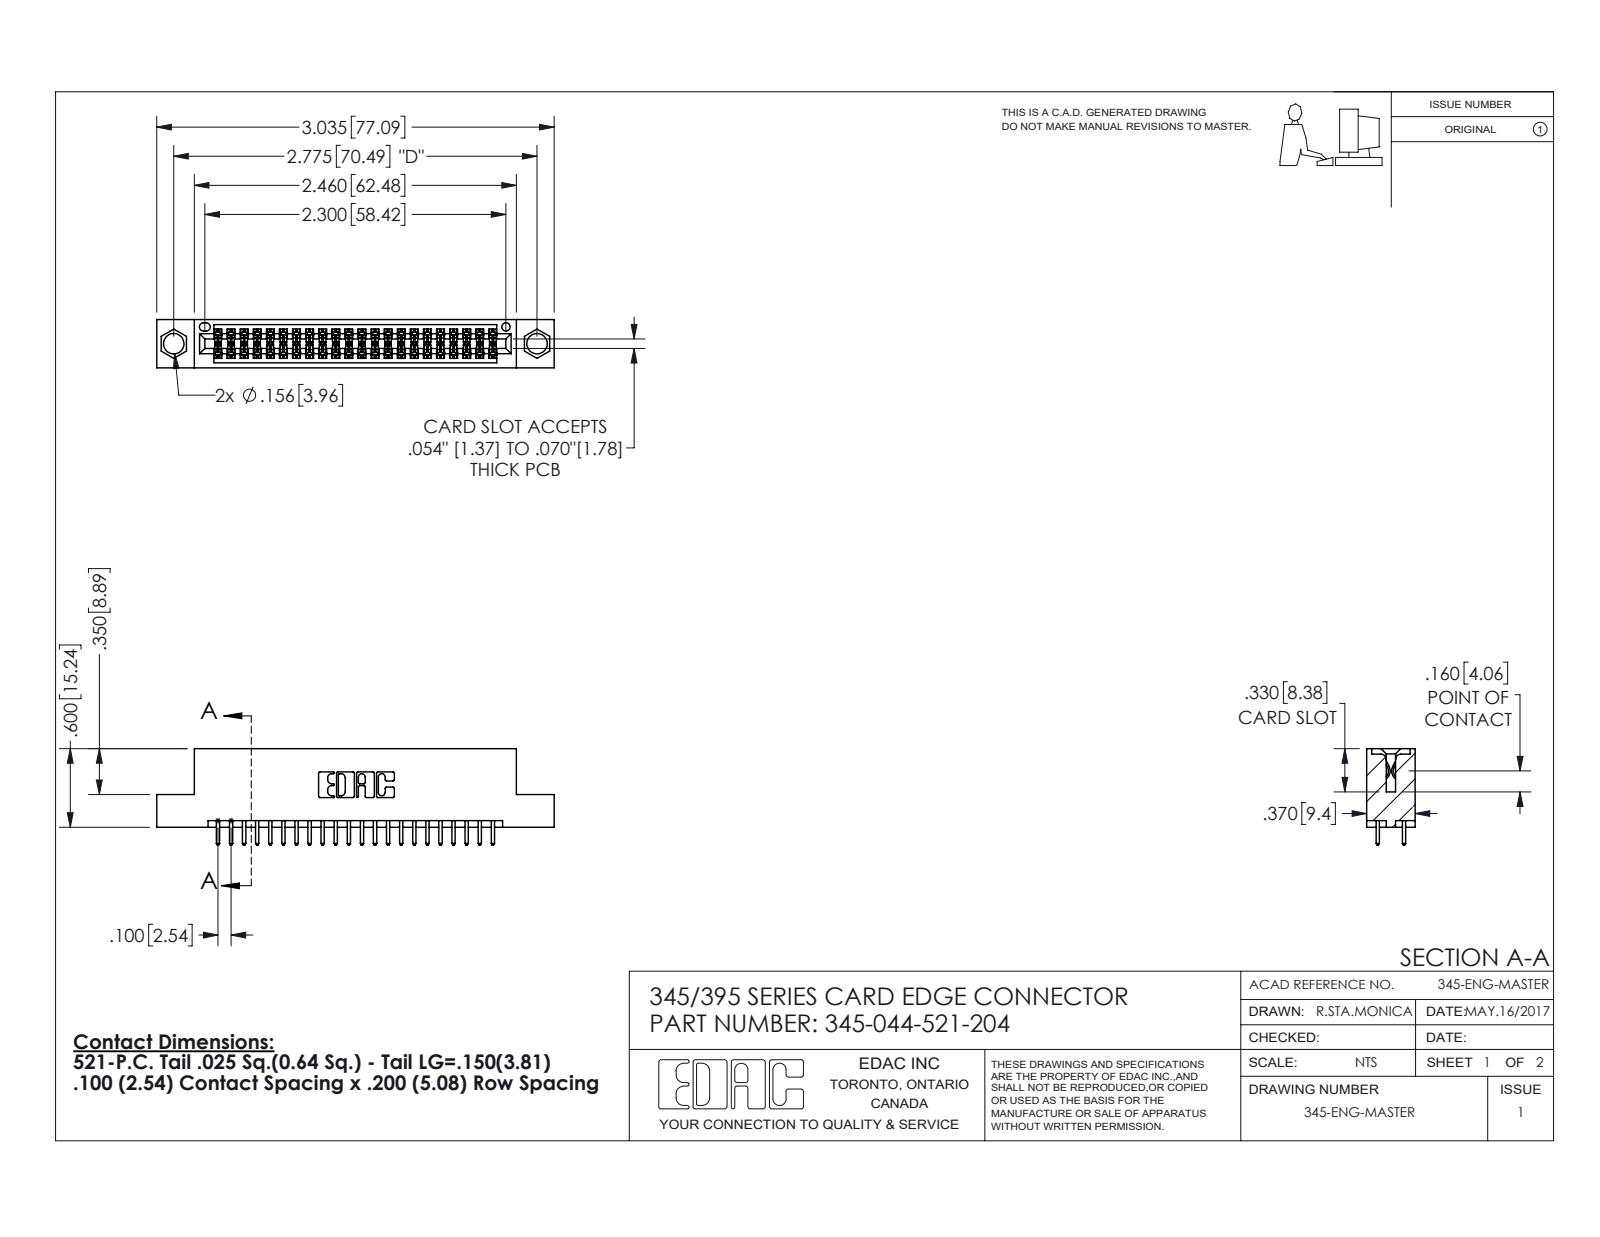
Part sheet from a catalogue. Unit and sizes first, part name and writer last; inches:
Units: inches
Overall size (bounding box): 3.035 × 0.737 × 0.37
Round holes (diameter × count): ⌀0.156 ×2, ⌀0.064 ×1
Partial cylindrical surfaces — rounded edges, fillets, slot ends (radius × count): R0.006 ×88, R0.01 ×44, R0.01 ×22, R0.007 ×6, R0.031 ×6, R0.026 ×3, R0.014 ×2, R0.019 ×2
Main face-to-face distances: 0.072, 0.298, 0.2, 0.37, 0.098, 0.272, 0.025, 0.225, 0.175, 0.149
Hole centre spacings: 0.27, 2.541, 2.775
Volume: 0.438 in³ · Surface area: 15.44 in²
Bodies: 45 solids, 2340 faces (1546 planar, 794 cylindrical, 0 other)
Part name (STEP PRODUCT): 345-292-001_345-293-121; 345 Part_Flush Mounting Lugs - 0.156 Dia-TI; 345-044-521-204
STEP written by: SolidWorks 2020 (CONFIG_CONTROL_DESIGN)
